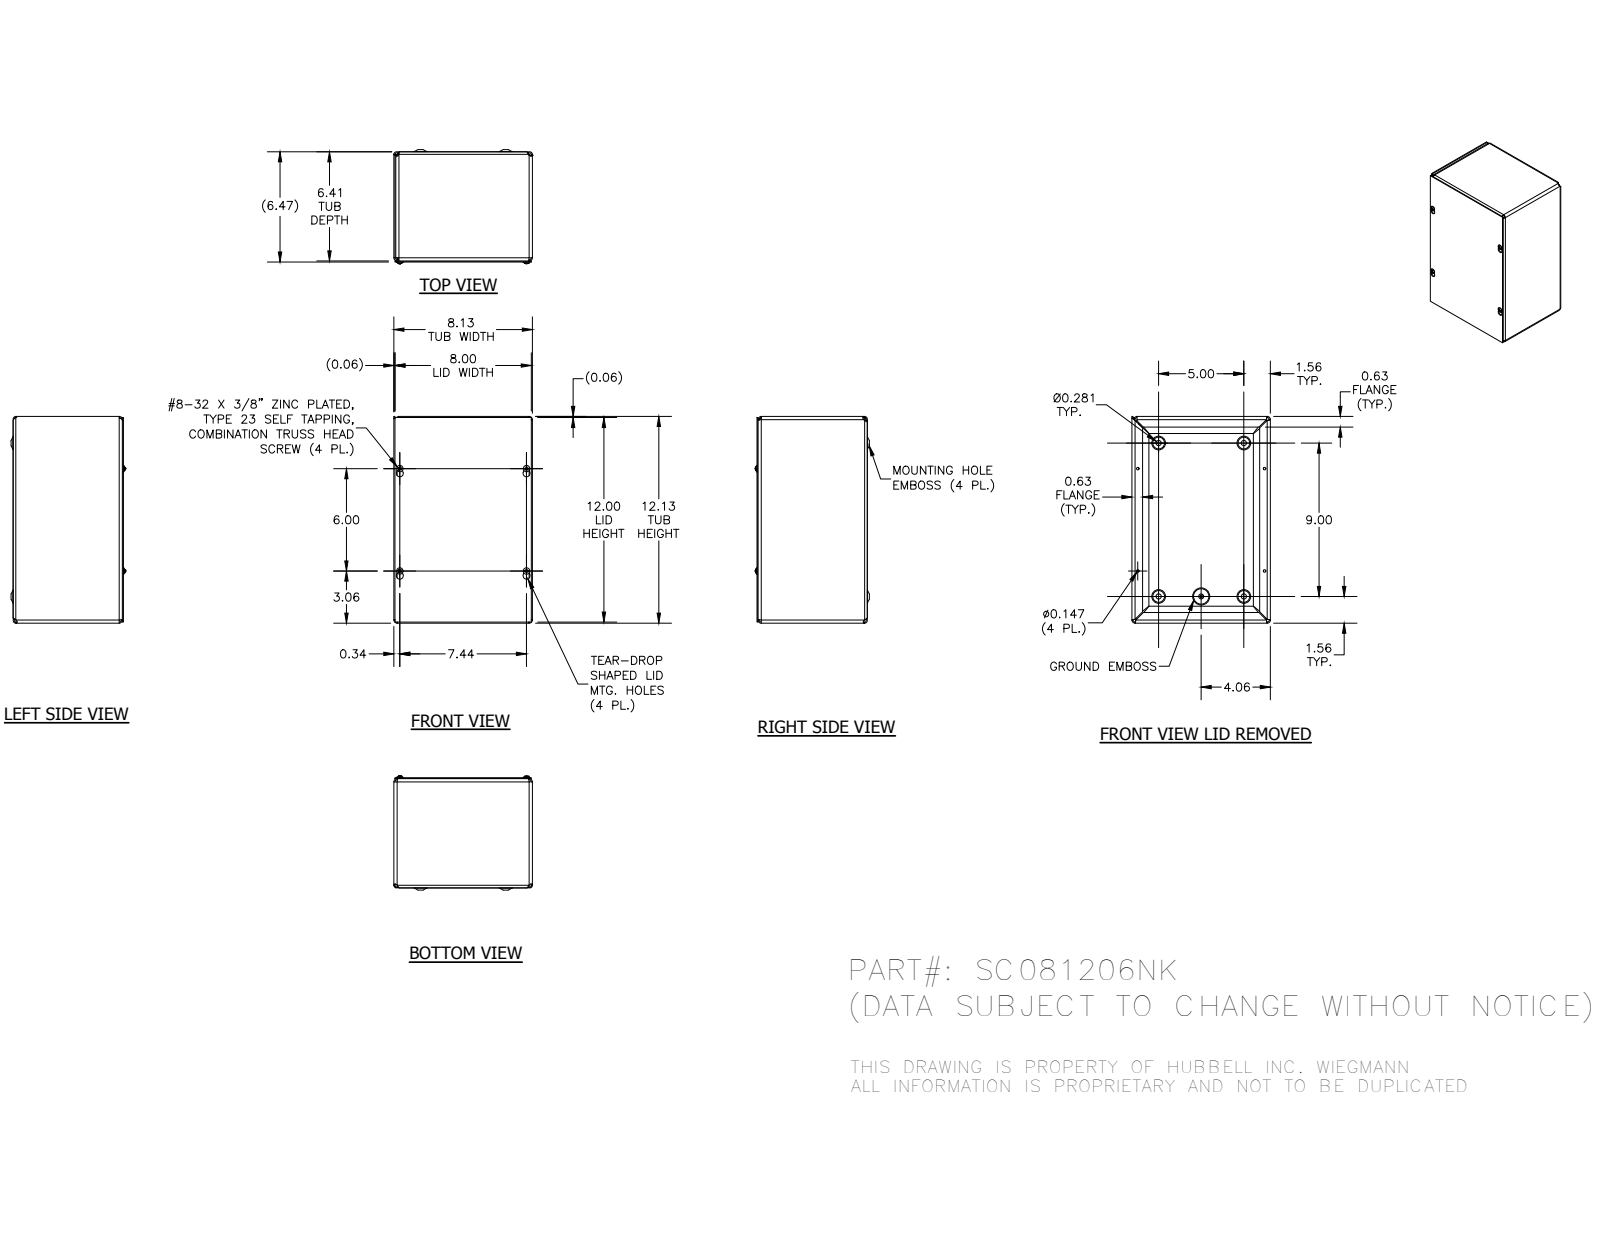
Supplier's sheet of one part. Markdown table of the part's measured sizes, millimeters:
| quantity | value |
| --- | --- |
| part name | SC0812BKP; SC081206NKWRA; SC0812LID; 34056 (+1 more) |
| STEP written by | Autodesk Inventor 2014 (AUTOMOTIVE_DESIGN) |
| units | millimeters |
| bodies | 7 solids, 357 faces (132 planar, 67 cylindrical, 158 other) |
| overall size | 307.98 × 206.38 × 170 |
| volume | 502 919 mm³ |
| surface area | 645 978 mm² |
| round holes (diameter × count) | 3.73 × 4, 7.62 × 4, 4.19 × 1 |
| round bosses / shafts (diameter × count) | 9.75 × 4, 4.17 × 4, 5.8 × 1 |
| partial cylindrical surfaces (radius × count) | 3.17 × 12, 4.75 × 8, 1.4 × 4, 1.57 × 4, 2.38 × 4, 2.97 × 4, 3.15 × 4, 3.96 × 4 |
| main face-to-face distances | 1.57, 204.8, 161.12, 162.69, 1.59, 162.71, 164.28, 203.23, 206.37, 1.58 |
| hole center spacings | 49.09, 193, 63.5, 101.85, 127, 152.4, 162.48, 162.49 |
